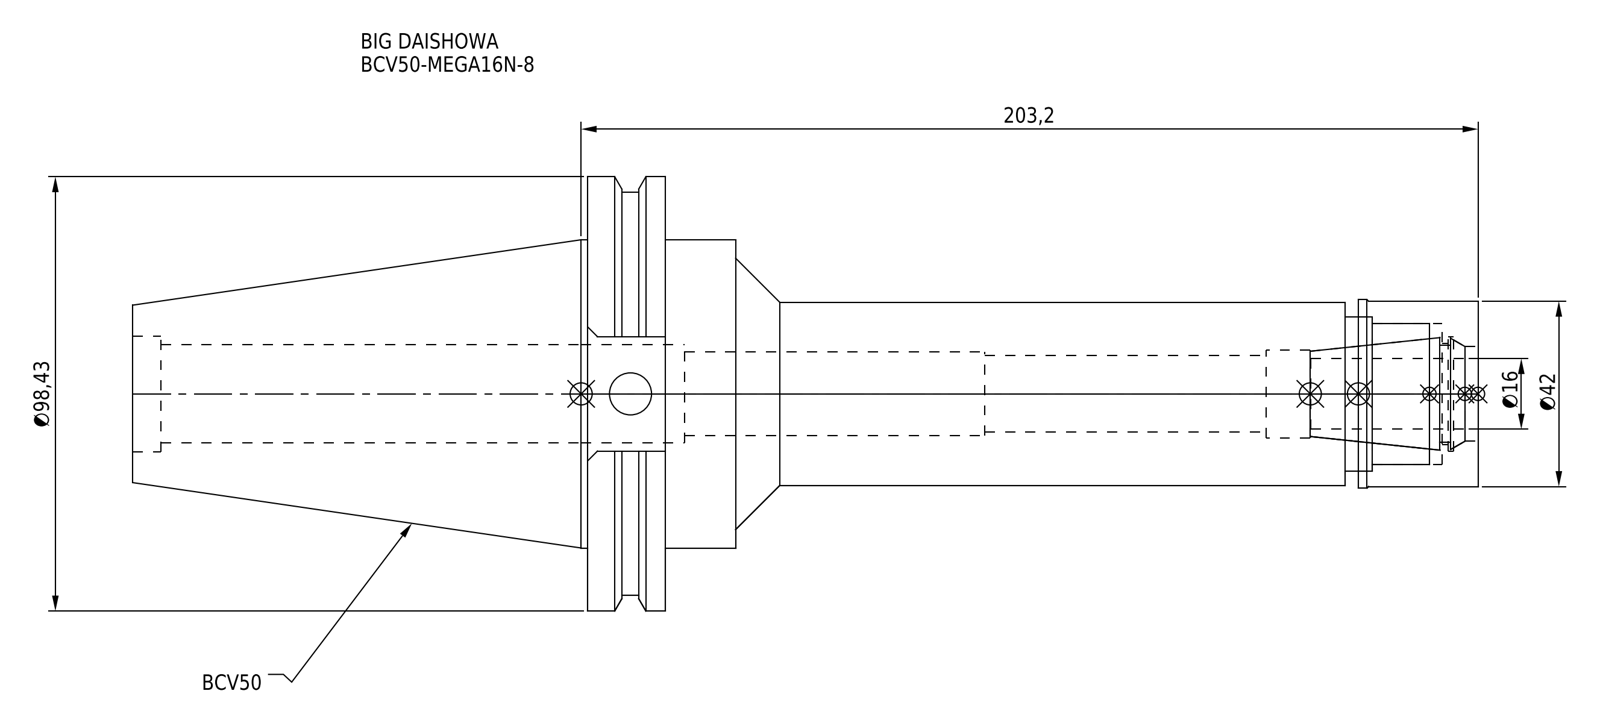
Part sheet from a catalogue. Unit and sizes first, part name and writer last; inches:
Units: inches
Overall size (bounding box): 12 × 3.875 × 3.738
Round holes (diameter × count): ⌀0.375 ×1, ⌀0.681 ×1, ⌀0.748 ×1, ⌀0.787 ×1, ⌀0.846 ×1, ⌀0.878 ×1, ⌀0.906 ×1, ⌀1.024 ×1, ⌀1.033 ×1, ⌀1.26 ×1, ⌀1.378 ×1
Round bosses / shafts (diameter × count): ⌀3.875 ×1, ⌀3.594 ×1, ⌀2.75 ×1, ⌀1.681 ×1, ⌀1.654 ×1, ⌀1.634 ×1
Main face-to-face distances: 0.691, 7.25, 7.941, 6.622, 0.628, 1.319, 12, 5.378, 4.75, 4.059
Volume: 34.41 in³ · Surface area: 133.4 in²
Bodies: 2 solids, 91 faces (33 planar, 44 cylindrical, 14 other)
Part name (STEP PRODUCT): BCV50MN16080-160_ASM.stp; BCV50-MEGA16N-8; BCV50-MEGA16N-8-160.stp; BCV50-MEGA16N-8-160-FreeParts (+3 more)
STEP written by: SolidWorks 2019 (CONFIG_CONTROL_DESIGN)
